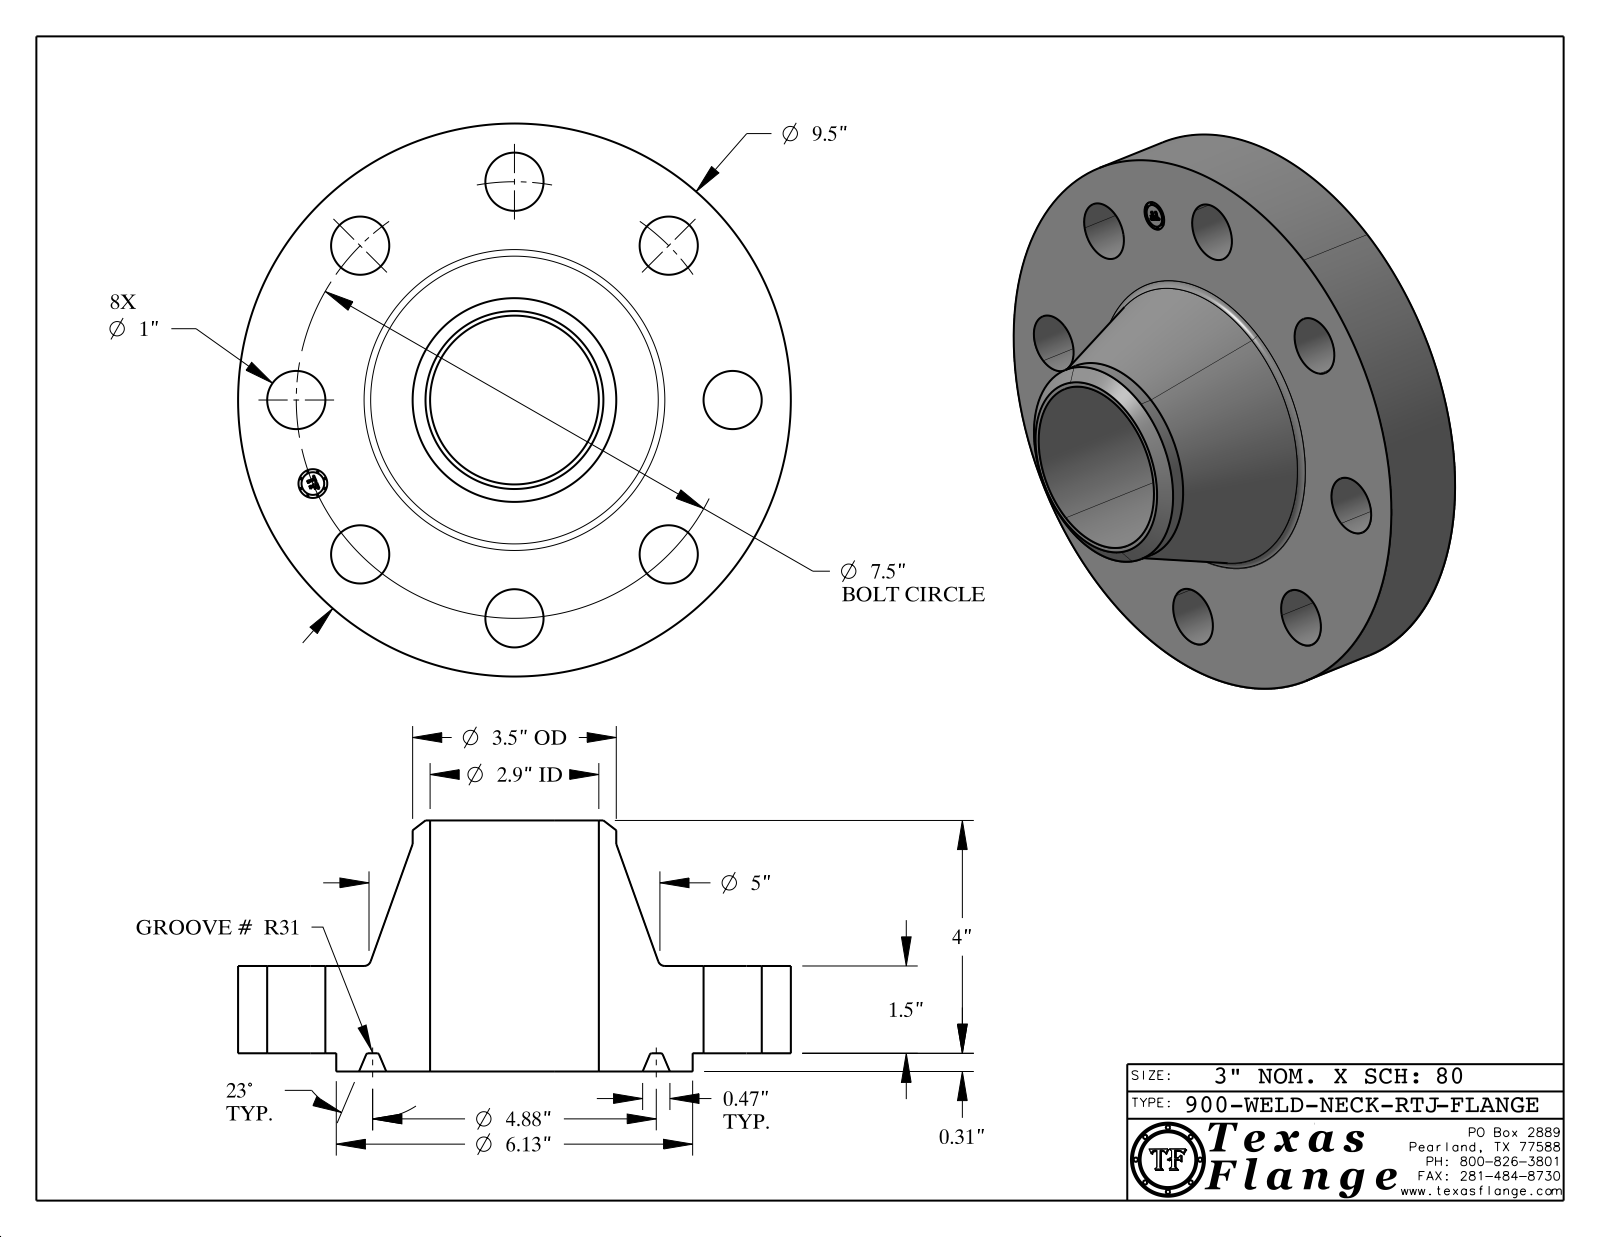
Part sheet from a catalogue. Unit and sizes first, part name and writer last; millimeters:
Units: millimetres
Overall size (bounding box): 241.3 × 241.3 × 109.6
Round holes (diameter × count): ⌀25.4 ×8, ⌀12.6 ×1, ⌀73.7 ×1
Round bosses / shafts (diameter × count): ⌀0.8 ×8, ⌀241.3 ×1, ⌀155.6 ×1, ⌀88.9 ×1, ⌀9.9 ×1
Main face-to-face distances: 38.1, 8, 46.1, 109.6, 101.6, 63.5, 0.4, 45.7, 37.7, 63.9
Hole centre spacings: 95.3, 72.9, 134.7, 176, 37.2, 158.4, 186.8, 190.5
Volume: 1 799 000 mm³ · Surface area: 175 900 mm²
Bodies: 1 solid, 429 faces (371 planar, 44 cylindrical, 14 other)
Part name (STEP PRODUCT): 900-WELD-NECK-RTJ
STEP written by: CATIA V5 STEP AP214 (AUTOMOTIVE_DESIGN)
